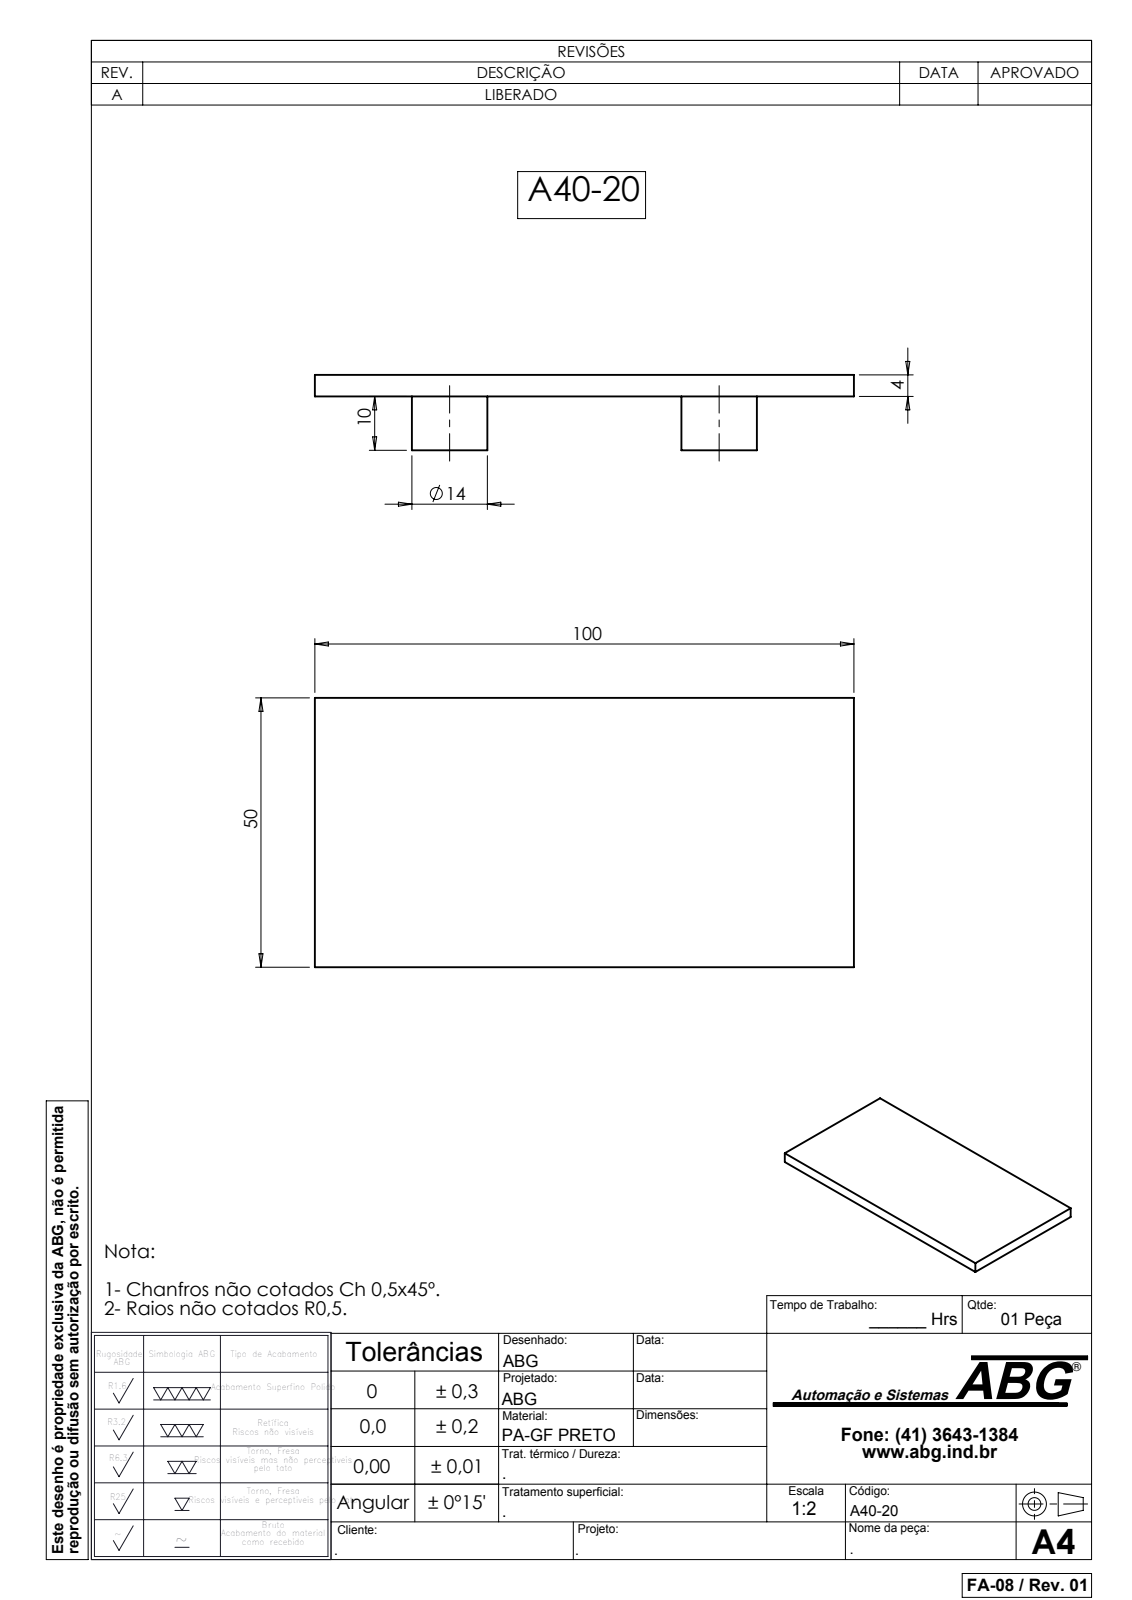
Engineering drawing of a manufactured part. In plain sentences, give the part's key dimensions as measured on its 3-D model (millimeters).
The part is named "A40-20". Its 3-D file was written by "SolidWorks 2007 (CONFIG_CONTROL_DESIGN)". It is 1 solid with 18 faces: 10 planar, 8 cylindrical and 0 other. Overall it measures 100 by 50 by 14 millimeters. Its volume is 20 817 cubic millimeters and its surface area 12 834 square millimeters. Round holes: 2 of diameter 12. Round bosses or shafts: 2 of diameter 14. The main face-to-face distances are 4, 50, 100, 14, 10. The hole center spacings are 50.
